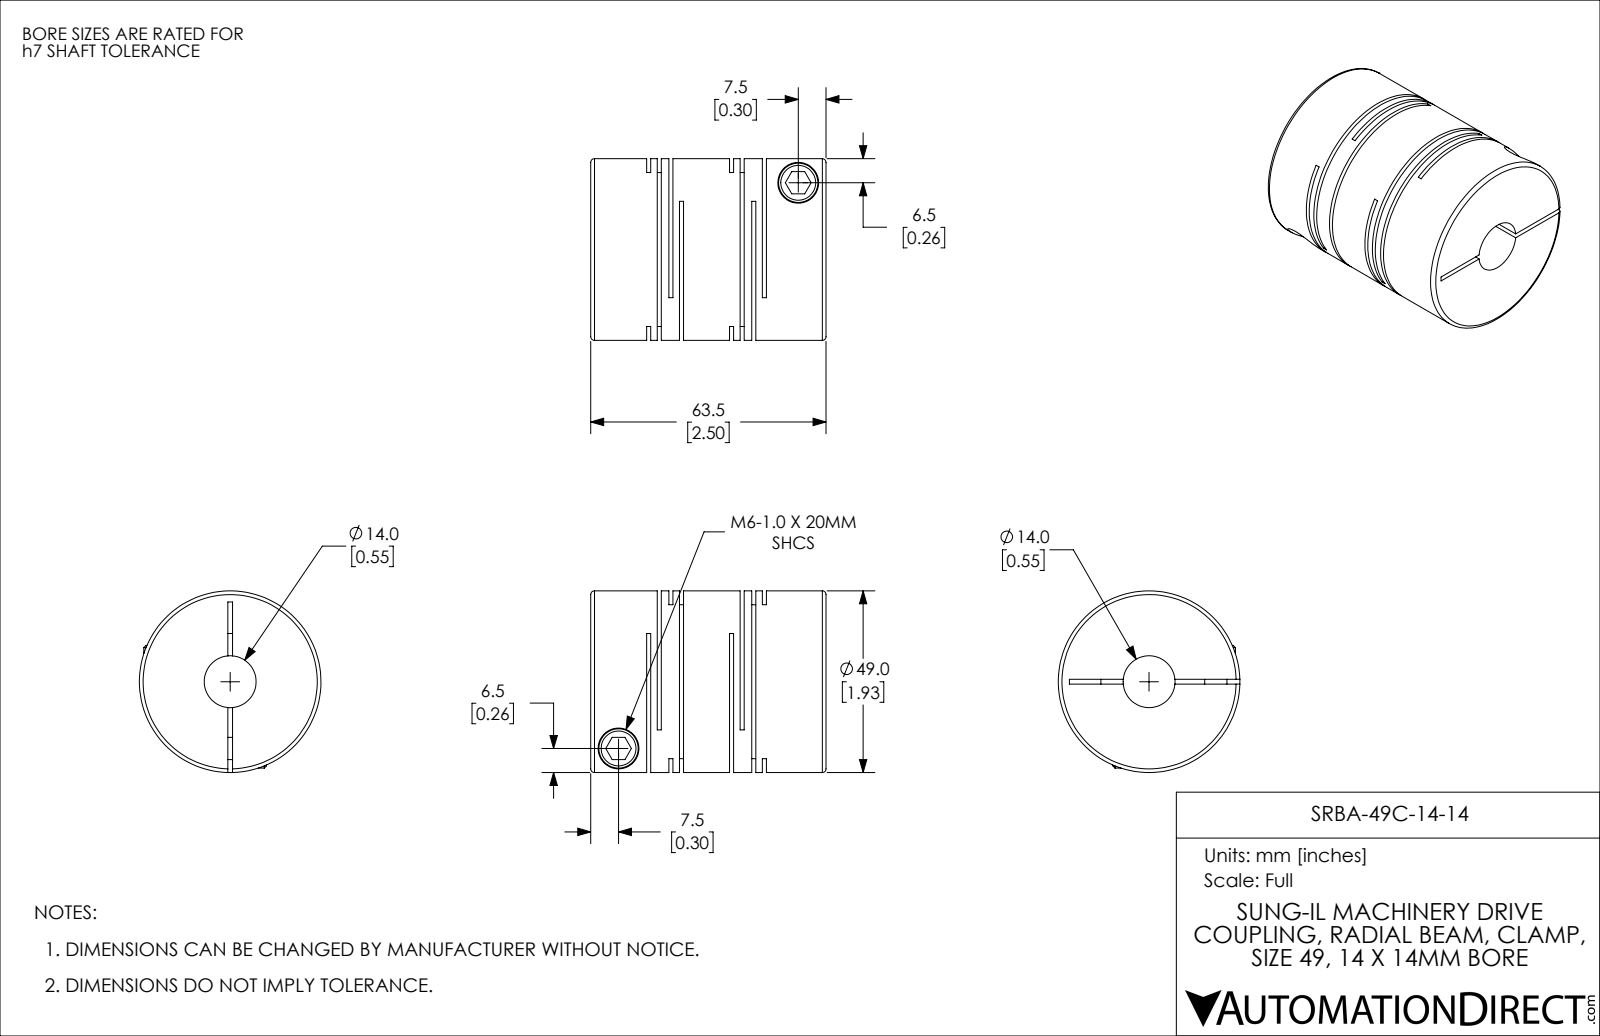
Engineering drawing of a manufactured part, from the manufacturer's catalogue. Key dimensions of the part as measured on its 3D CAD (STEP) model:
Part name (STEP PRODUCT): SRBA-49C-14-14
STEP written by: SolidWorks 2021 (CONFIG_CONTROL_DESIGN)
Units: millimetres
Bodies: 1 solid, 114 faces (60 planar, 42 cylindrical, 12 other)
Overall size (bounding box): 63.5 × 49 × 49
Volume: 94 750 mm³ · Surface area: 40 166 mm²
Round holes (diameter × count): ⌀6 ×2, ⌀11 ×2, ⌀14 ×1
Round bosses / shafts (diameter × count): ⌀10.6 ×2, ⌀49 ×1
Main face-to-face distances: 6, 1.1, 2.85, 22.35, 1.75, 4.9, 21.25, 3.15, 19.5, 16.35
